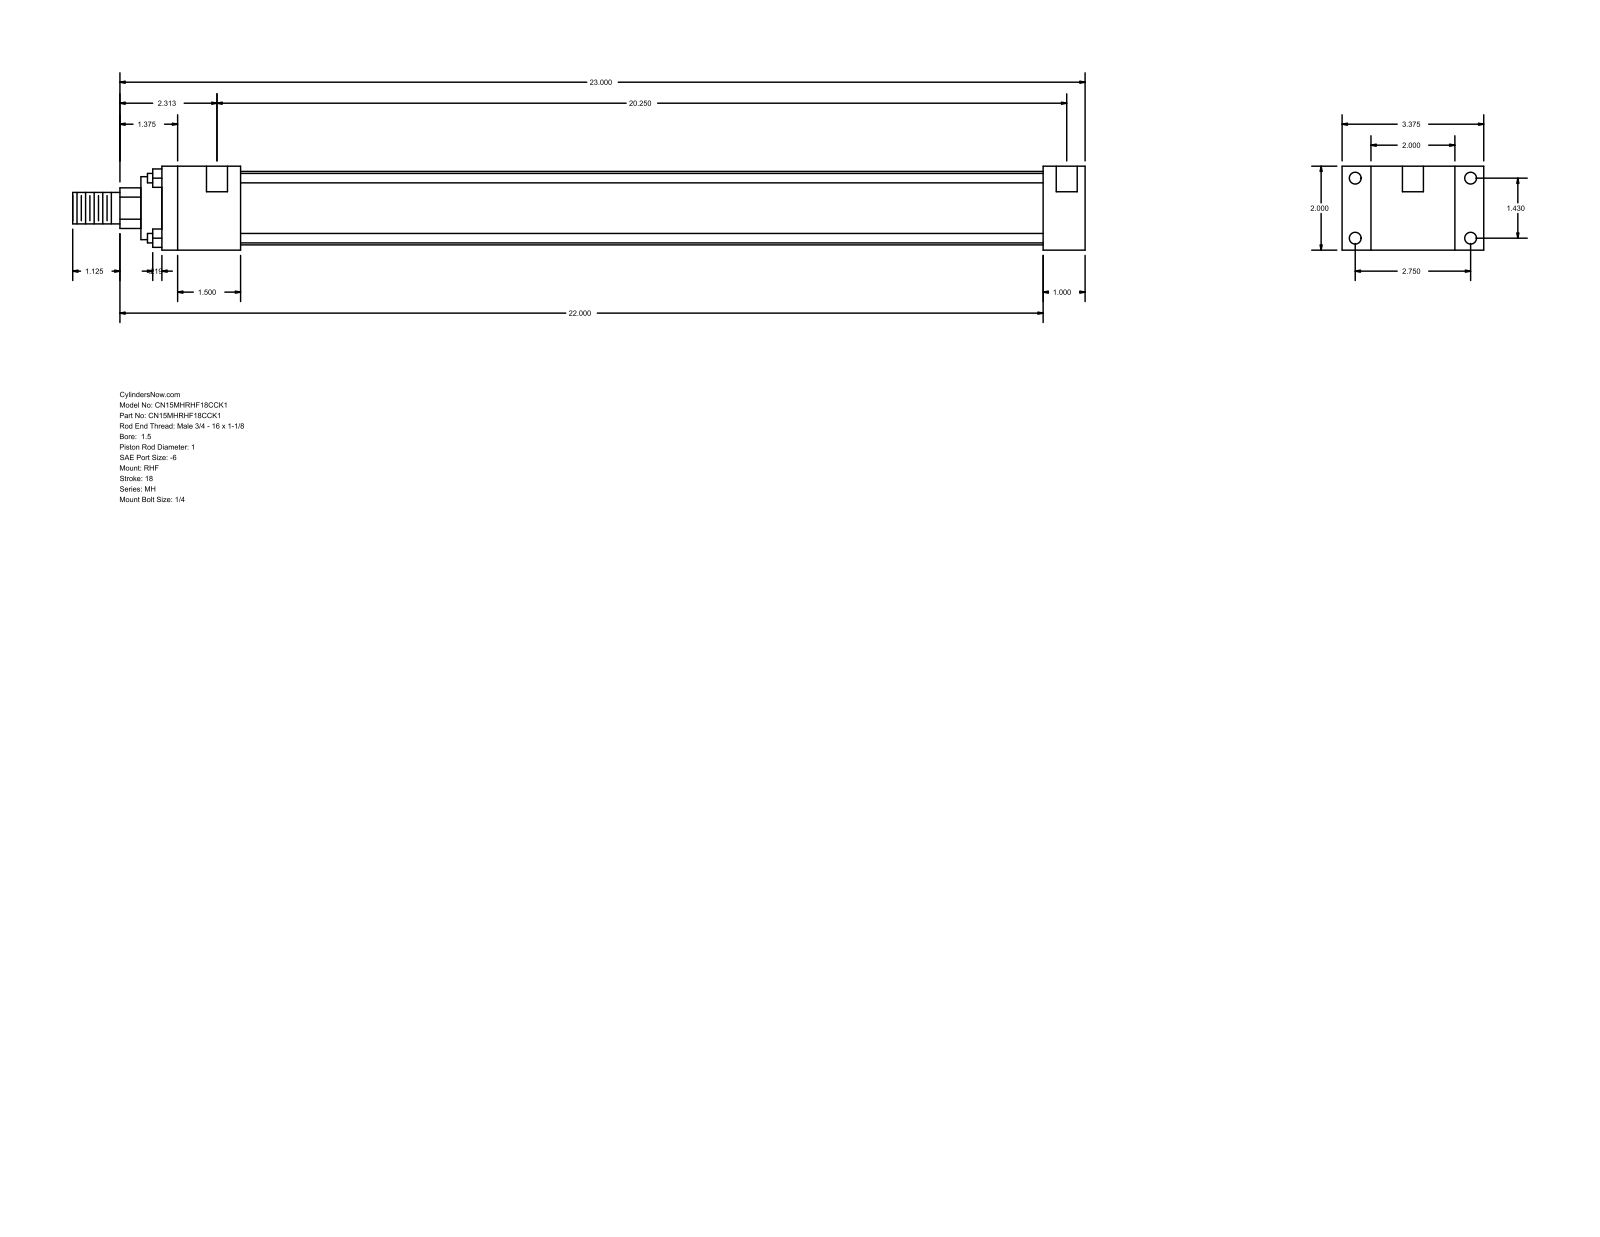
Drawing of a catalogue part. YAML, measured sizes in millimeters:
part_name: "MH_RHF__0150_1"
step_written_by: "GSSL Pune (CONFIG_CONTROL_DESIGN)"
units: millimeters
bodies: {solids: 0, faces: 88, planar: 60, cylindrical: 28, other: 0}
overall_size: [612.77, 85.72, 50.8]
round_holes:
  - {diameter: 5.56, count: 4}
  - {diameter: 7.14, count: 4}
  - {diameter: 12.7, count: 2}
round_bosses_or_shafts:
  - {diameter: 5.71, count: 4}
  - {diameter: 44.45, count: 1}
  - {diameter: 38.1, count: 1}
  - {diameter: 25.4, count: 1}
  - {diameter: 19.05, count: 1}
partial_cylinders:
  - {radius: 12.29, count: 1}
face_to_face_distances: [50.8, 25.4, 17.46, 68.26, 85.72, 558.8, 533.4, 47.63, 485.77, 511.17]
hole_center_spacings: [36.32, 69.84, 78.72, 517.53, 3.18, 514.35]
